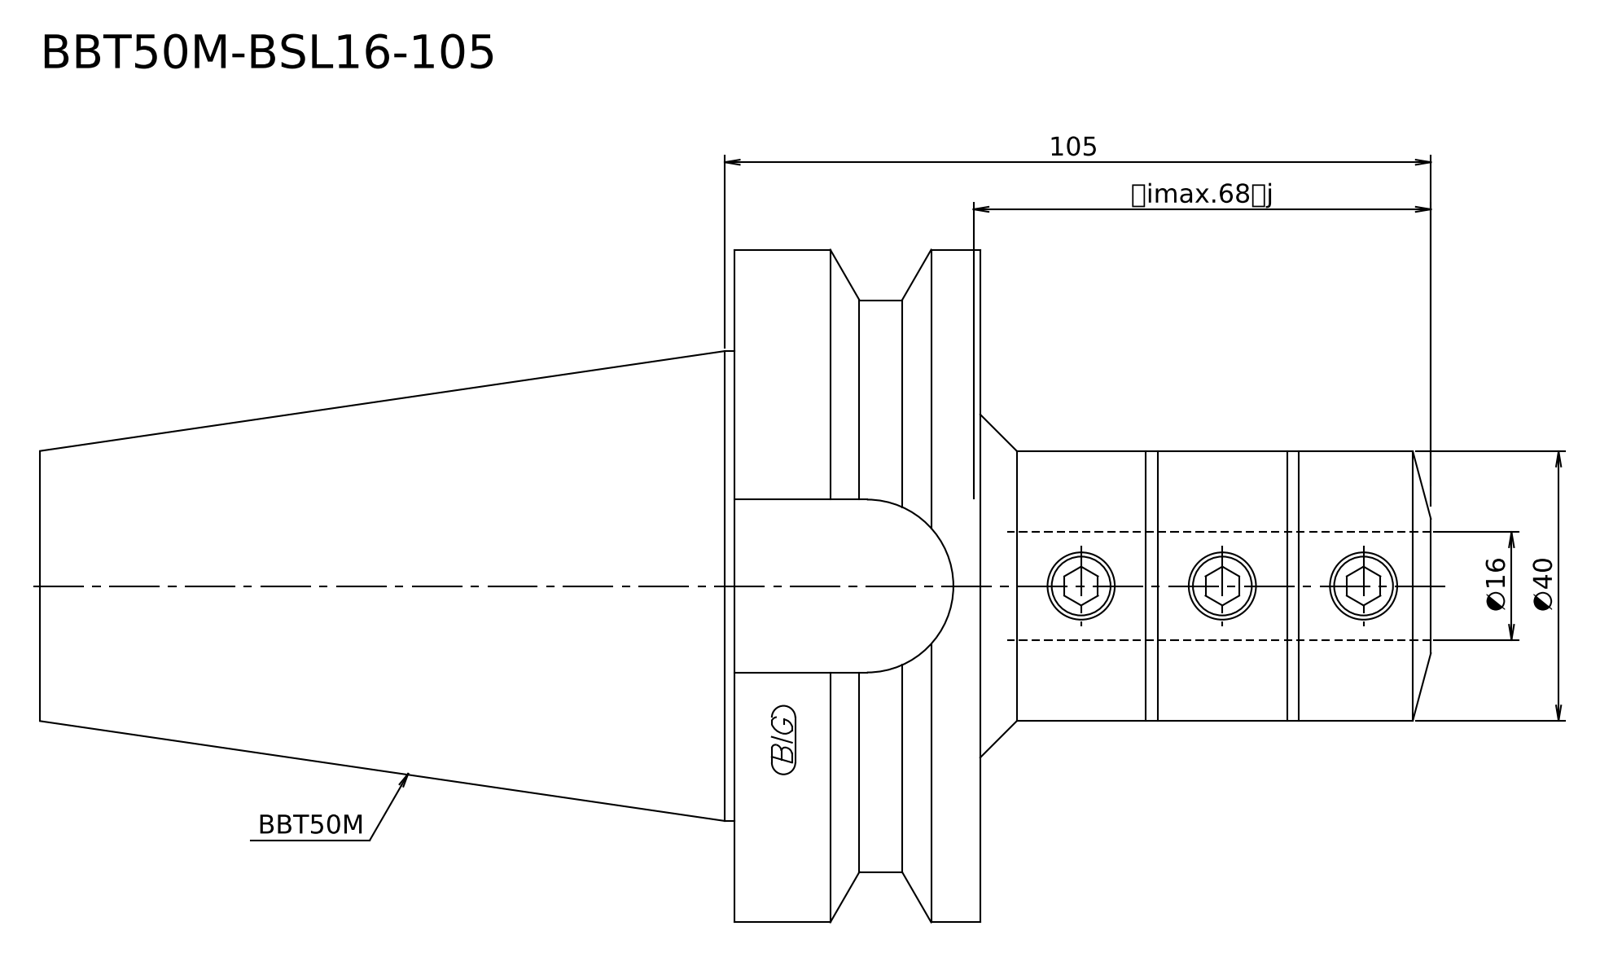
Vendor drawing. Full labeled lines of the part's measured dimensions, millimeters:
STEP written by: Kubotek KeyCreator 2011 V10.0.2 (22737) (automotive_design)
Units: millimetres
Bodies: 1 solid, 14 faces (4 planar, 5 cylindrical, 5 other)
Overall size (bounding box): 206.8 × 100 × 100
Volume: 601 545 mm³ · Surface area: 52 480 mm²
Round bosses / shafts (diameter × count): ⌀100 ×1, ⌀85 ×1, ⌀69.85 ×1, ⌀40 ×1
Main face-to-face distances: 36.5, 139.8, 103.3, 67, 103.5, 206.8
